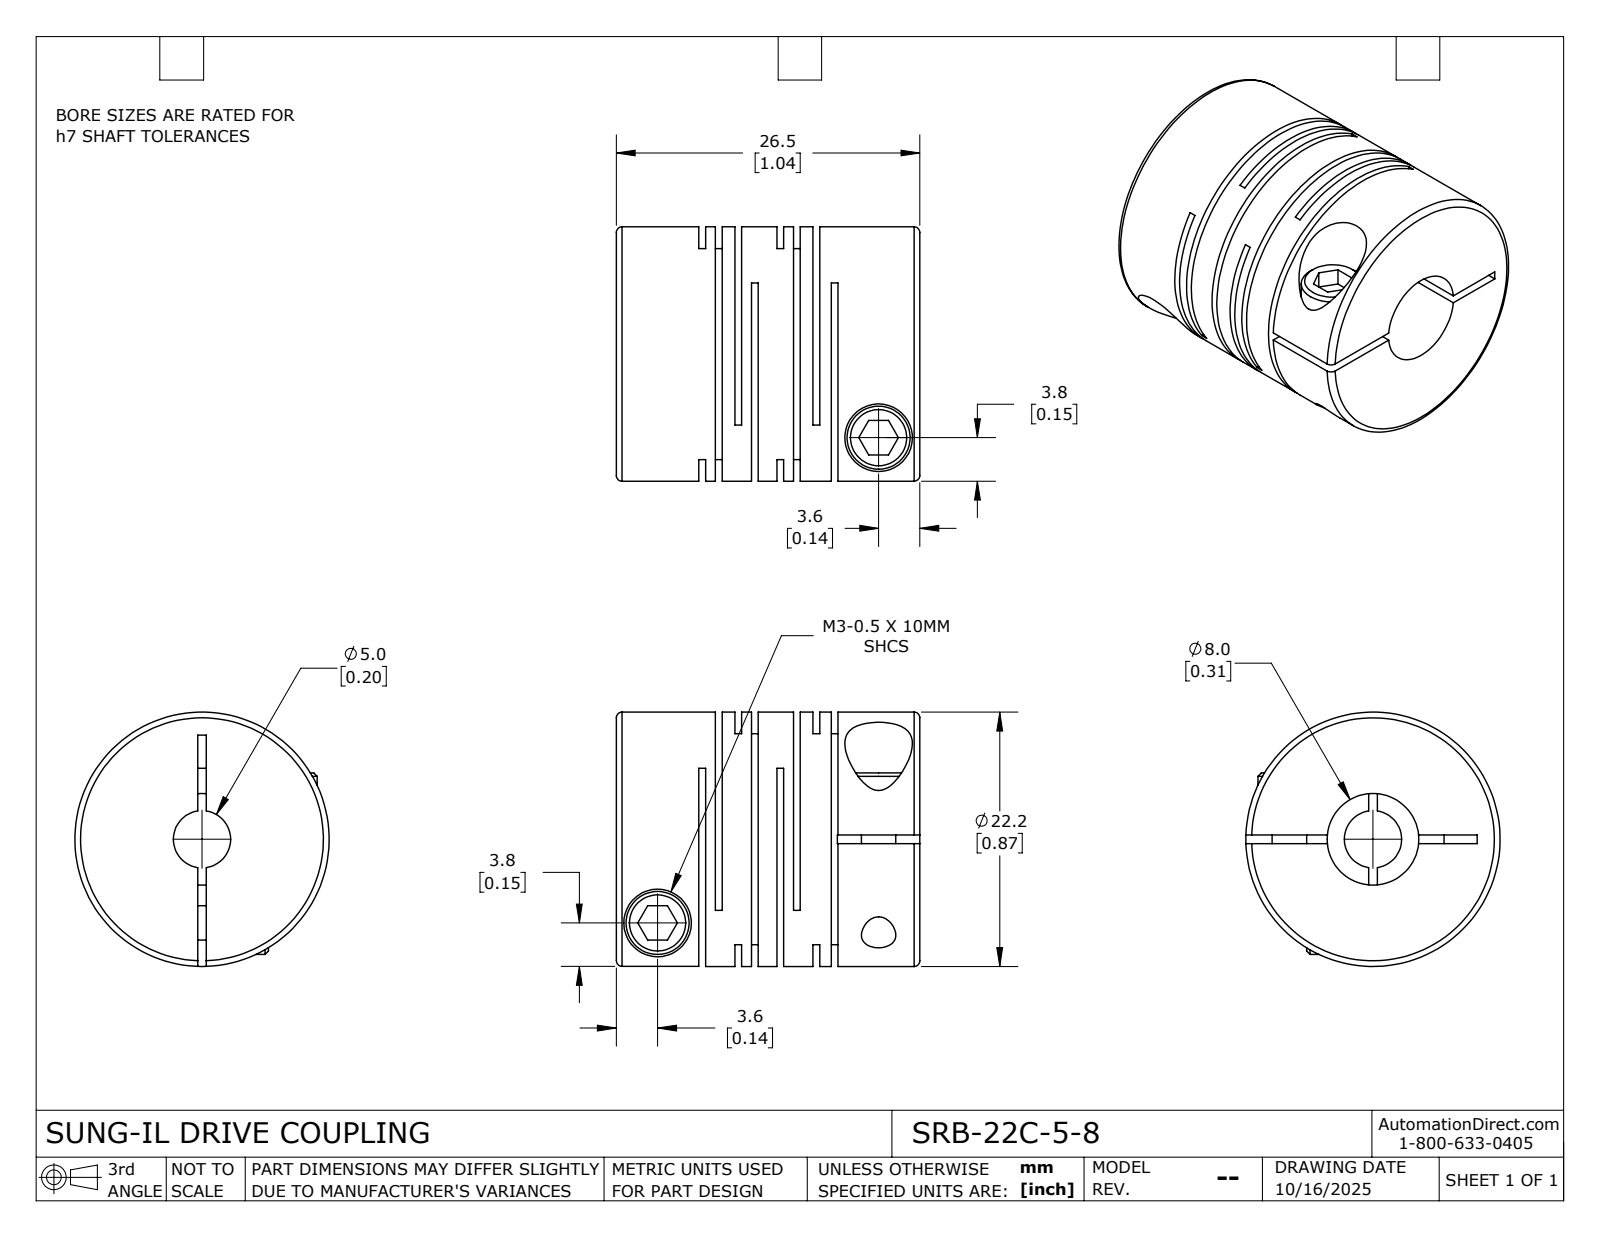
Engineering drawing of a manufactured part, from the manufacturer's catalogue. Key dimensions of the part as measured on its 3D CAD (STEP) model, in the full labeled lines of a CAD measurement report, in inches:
Part name (STEP PRODUCT): SRB-22C-5-8
STEP written by: SolidWorks 2024 (CONFIG_CONTROL_DESIGN)
Units: inches
Bodies: 1 solid, 115 faces (60 planar, 42 cylindrical, 13 other)
Overall size (bounding box): 1.043 × 0.874 × 0.874
Volume: 0.459 in³ · Surface area: 12.2 in²
Round holes (diameter × count): ⌀0.118 ×2, ⌀0.232 ×2, ⌀0.197 ×1, ⌀0.315 ×1
Round bosses / shafts (diameter × count): ⌀0.217 ×2, ⌀0.874 ×1
Main face-to-face distances: 0.023, 0.269, 0.057, 0.124, 0.211, 0.067, 0.144, 0.08, 0.292, 0.245
